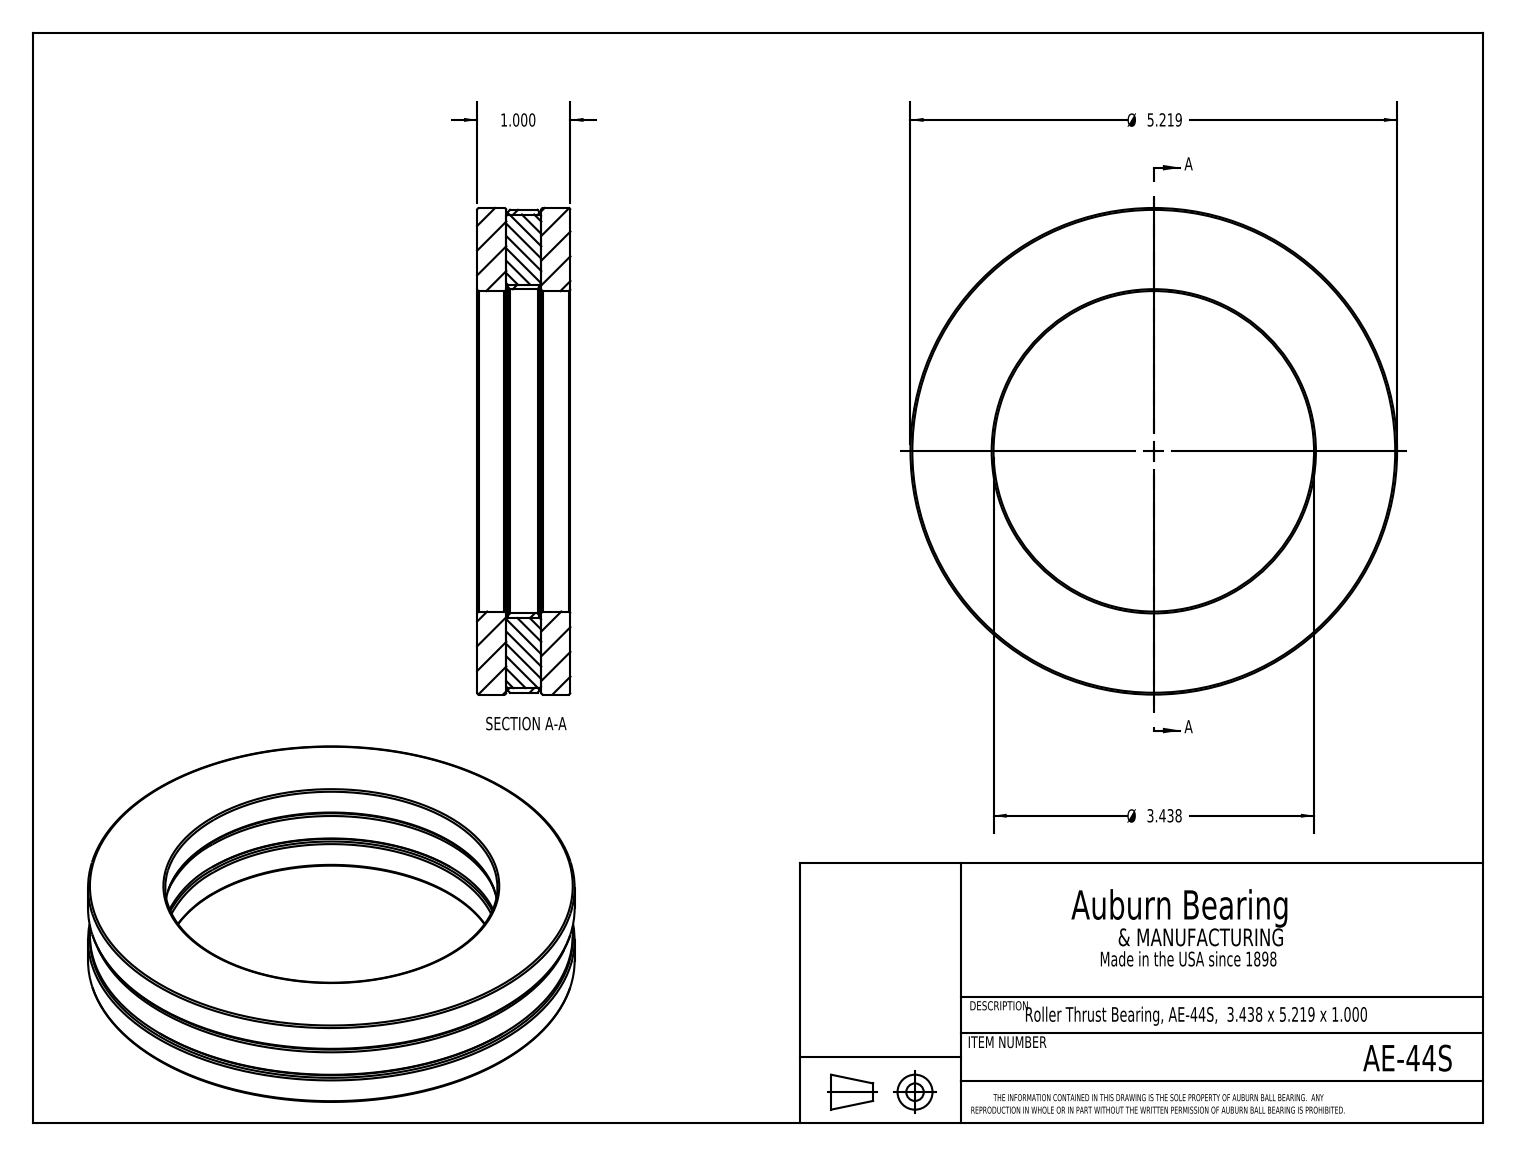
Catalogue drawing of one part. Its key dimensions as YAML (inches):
part_name: "AE-44S"
step_written_by: "SolidWorks 2017 (CONFIG_CONTROL_DESIGN)"
units: inches
bodies: {solids: 7, faces: 60, planar: 30, cylindrical: 10, other: 20}
overall_size: [5.219, 5.219, 1]
volume: 11.38
surface_area: 101.2
round_holes:
  - {diameter: 3.437, count: 1}
  - {diameter: 3.477, count: 1}
round_bosses_or_shafts:
  - {diameter: 0.375, count: 2}
  - {diameter: 5.219, count: 1}
  - {diameter: 5.179, count: 1}
face_to_face_distances: [0.313, 0.687, 0.333, 0.667, 0.02, 0.355, 0.375, 1, 0.335, 1.601]
